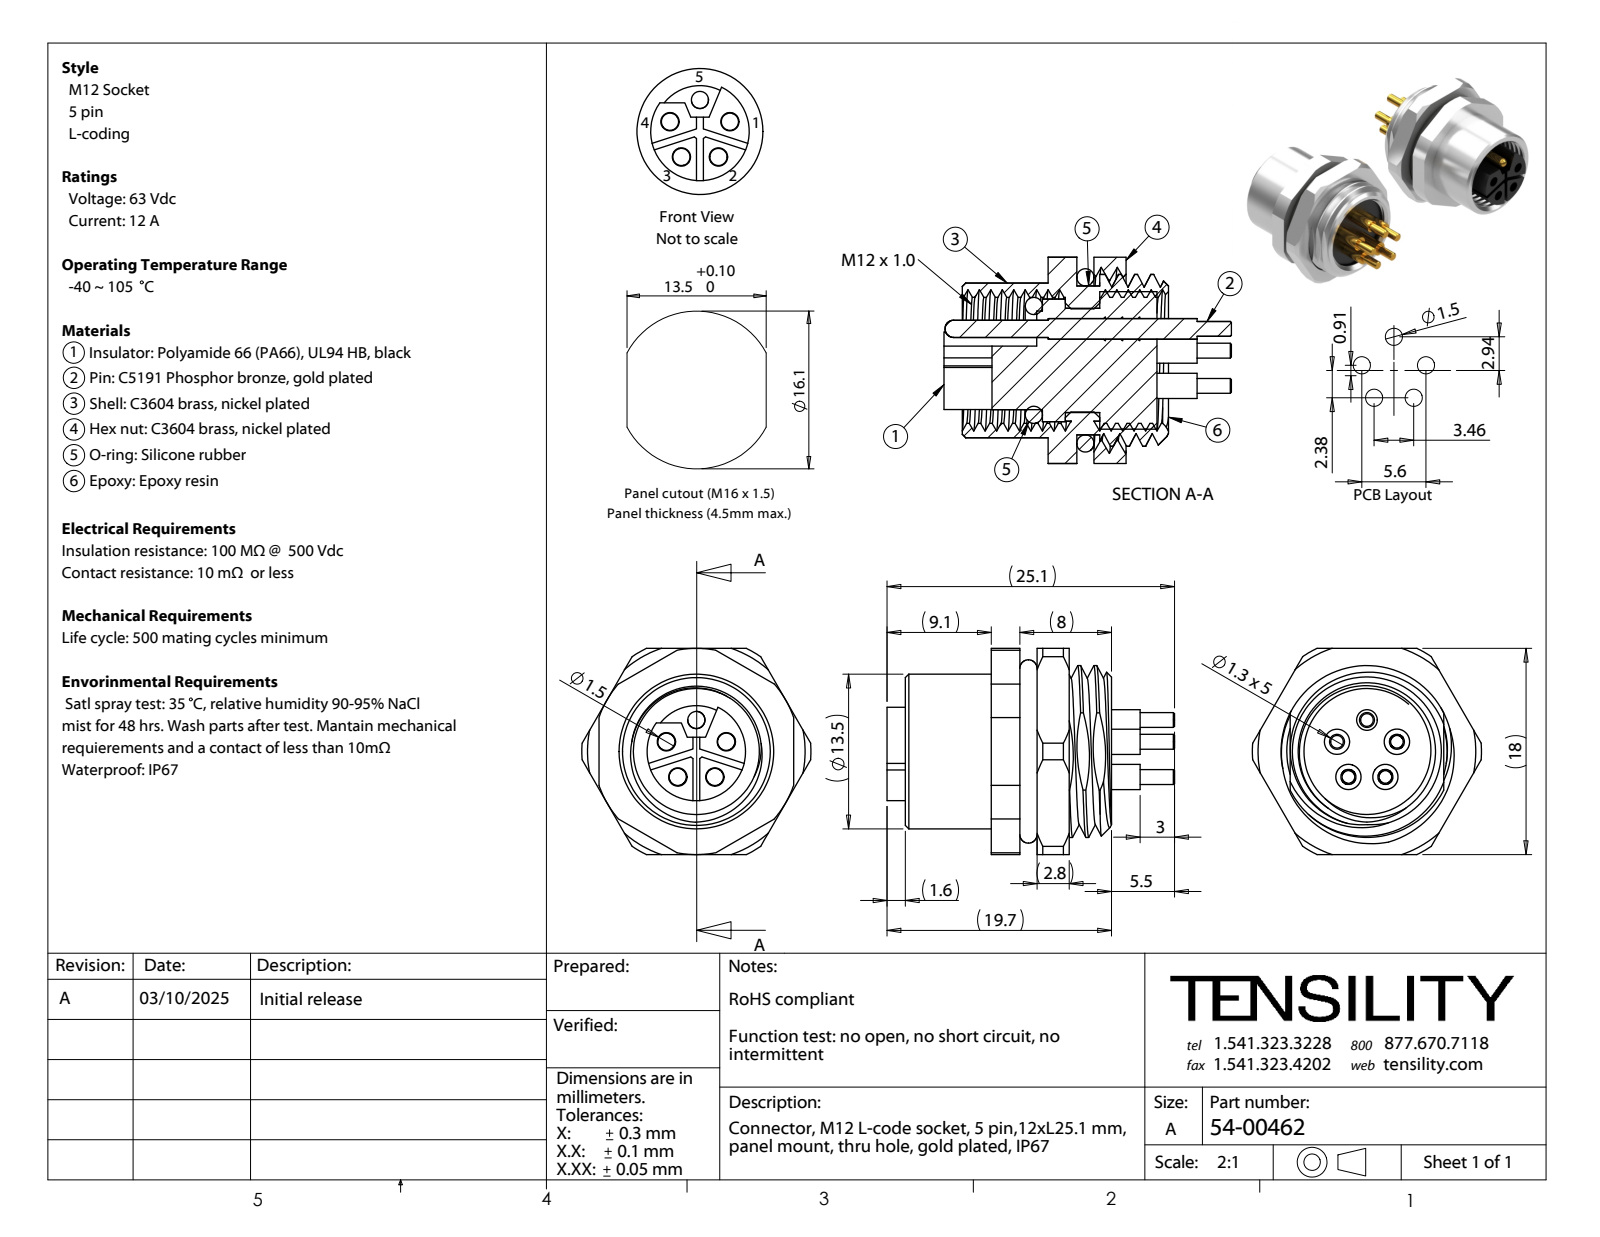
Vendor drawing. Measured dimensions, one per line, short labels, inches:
name: 54-00462-01; 54-00462-03; 54-00462-04; 54-00462-07 (+4 more)
written by: SolidWorks 2021 (CONFIG_CONTROL_DESIGN)
unit: in
bodies: 10 solids, 355 faces (116 planar, 145 cylindrical, 94 other)
size: 0.988 × 0.787 × 0.709
volume: 0.173 in³; area: 8.962 in²
holes: 5× ⌀0.059, 4× ⌀0.063, 1× ⌀0.354, 1× ⌀0.433, 1× ⌀0.551
bosses: 5× ⌀0.051, 4× ⌀0.087, 1× ⌀0.531, 1× ⌀0.512, 1× ⌀0.472, 1× ⌀0.421, 1× ⌀0.417, 1× ⌀0.358
rounds: 1× R0.295, 1× R0.354, 1× R0.394
face distances: 0.098, 0.276, 0.02, 0.197, 0.059, 0.177, 0.079, 0.091, 0.268, 0.217
hole spacings: 0.108, 0.206, 0.128, 0.127, 0.206
